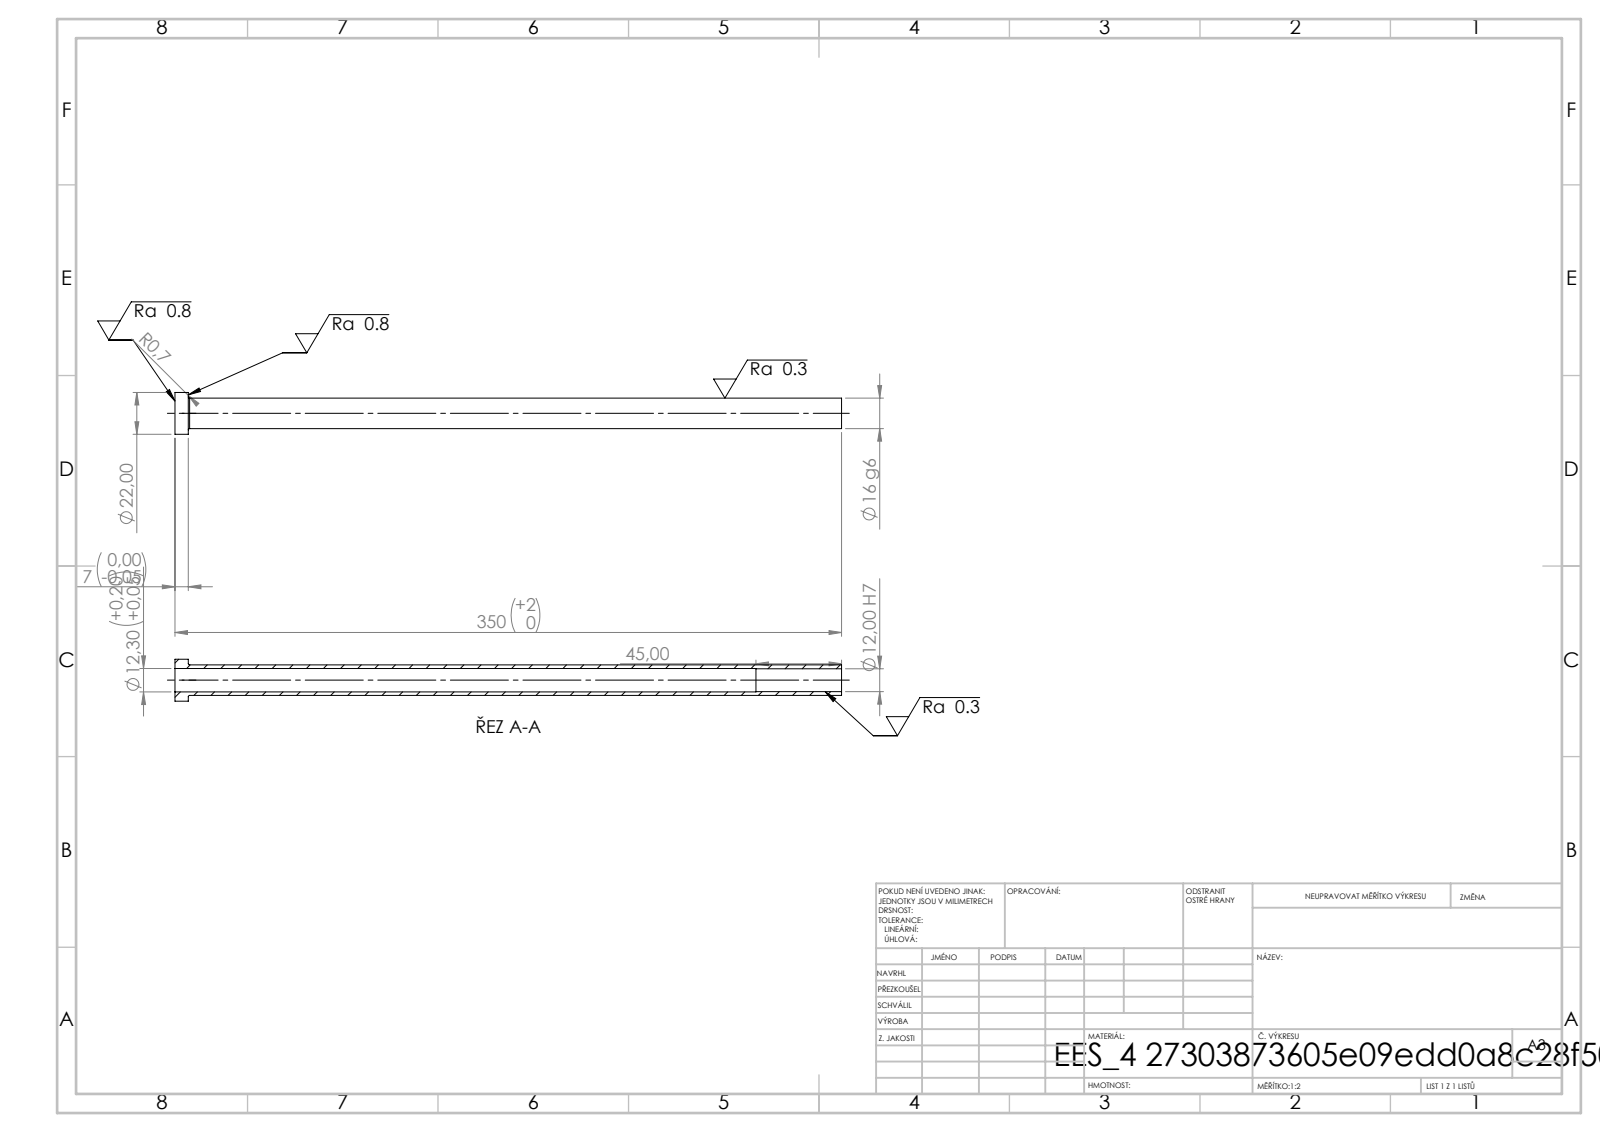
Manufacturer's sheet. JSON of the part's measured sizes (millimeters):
{"step_written_by": "SolidWorks 2019 (CONFIG_CONTROL_DESIGN)", "units": "millimeters", "bodies": {"solids": 1, "faces": 14, "planar": 4, "cylindrical": 8, "other": 2}, "overall_size": [350, 22, 22], "volume_mm3": 30300, "surface_area_mm2": 31726, "round_holes": [[12, 1], [12.3, 1]], "round_bosses_or_shafts": [[22, 1], [16, 1]], "face_to_face_distances": [7, 350, 343, 305, 298, 45]}
